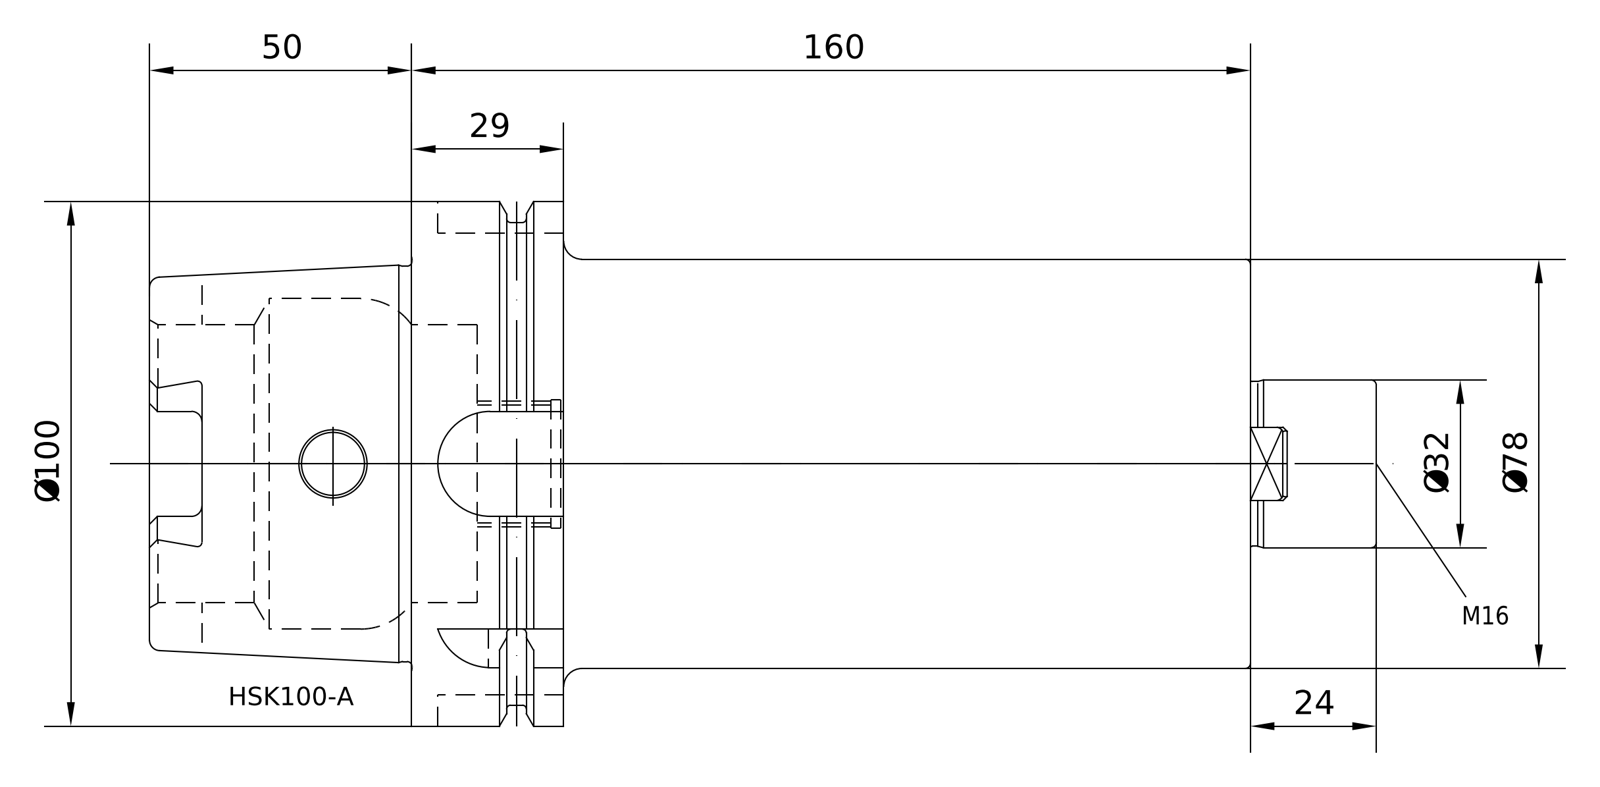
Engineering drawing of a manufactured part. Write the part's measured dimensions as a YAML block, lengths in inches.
part_name: "A100-052-32"
step_written_by: "PRO/ENGINEER BY PARAMETRIC TECHNOLOGY CORPORATION, 2010430 (CONFIG_CONTROL_DESIGN)"
units: inches
bodies: {solids: 1, faces: 191, planar: 61, cylindrical: 55, other: 75}
overall_size: [9.213, 3.937, 3.937]
volume: 54.7
surface_area: 137
round_holes:
  - {diameter: 0.394, count: 1}
  - {diameter: 0.472, count: 1}
  - {diameter: 0.551, count: 1}
  - {diameter: 0.63, count: 1}
  - {diameter: 0.886, count: 1}
  - {diameter: 0.945, count: 1}
  - {diameter: 0.957, count: 1}
  - {diameter: 0.965, count: 1}
  - {diameter: 2.087, count: 1}
  - {diameter: 2.48, count: 1}
round_bosses_or_shafts:
  - {diameter: 3.937, count: 1}
  - {diameter: 3.622, count: 1}
  - {diameter: 3.071, count: 1}
  - {diameter: 2.967, count: 1}
  - {diameter: 1.26, count: 1}
partial_cylinders:
  - {radius: 0.079, count: 6}
  - {radius: 0.197, count: 4}
  - {radius: 0.315, count: 1}
  - {radius: 0.394, count: 1}
  - {radius: 0.433, count: 1}
face_to_face_distances: [6.299, 1.142, 5.157, 0.492, 0.65, 5.807, 1.969, 2.461, 3.11, 8.268]
